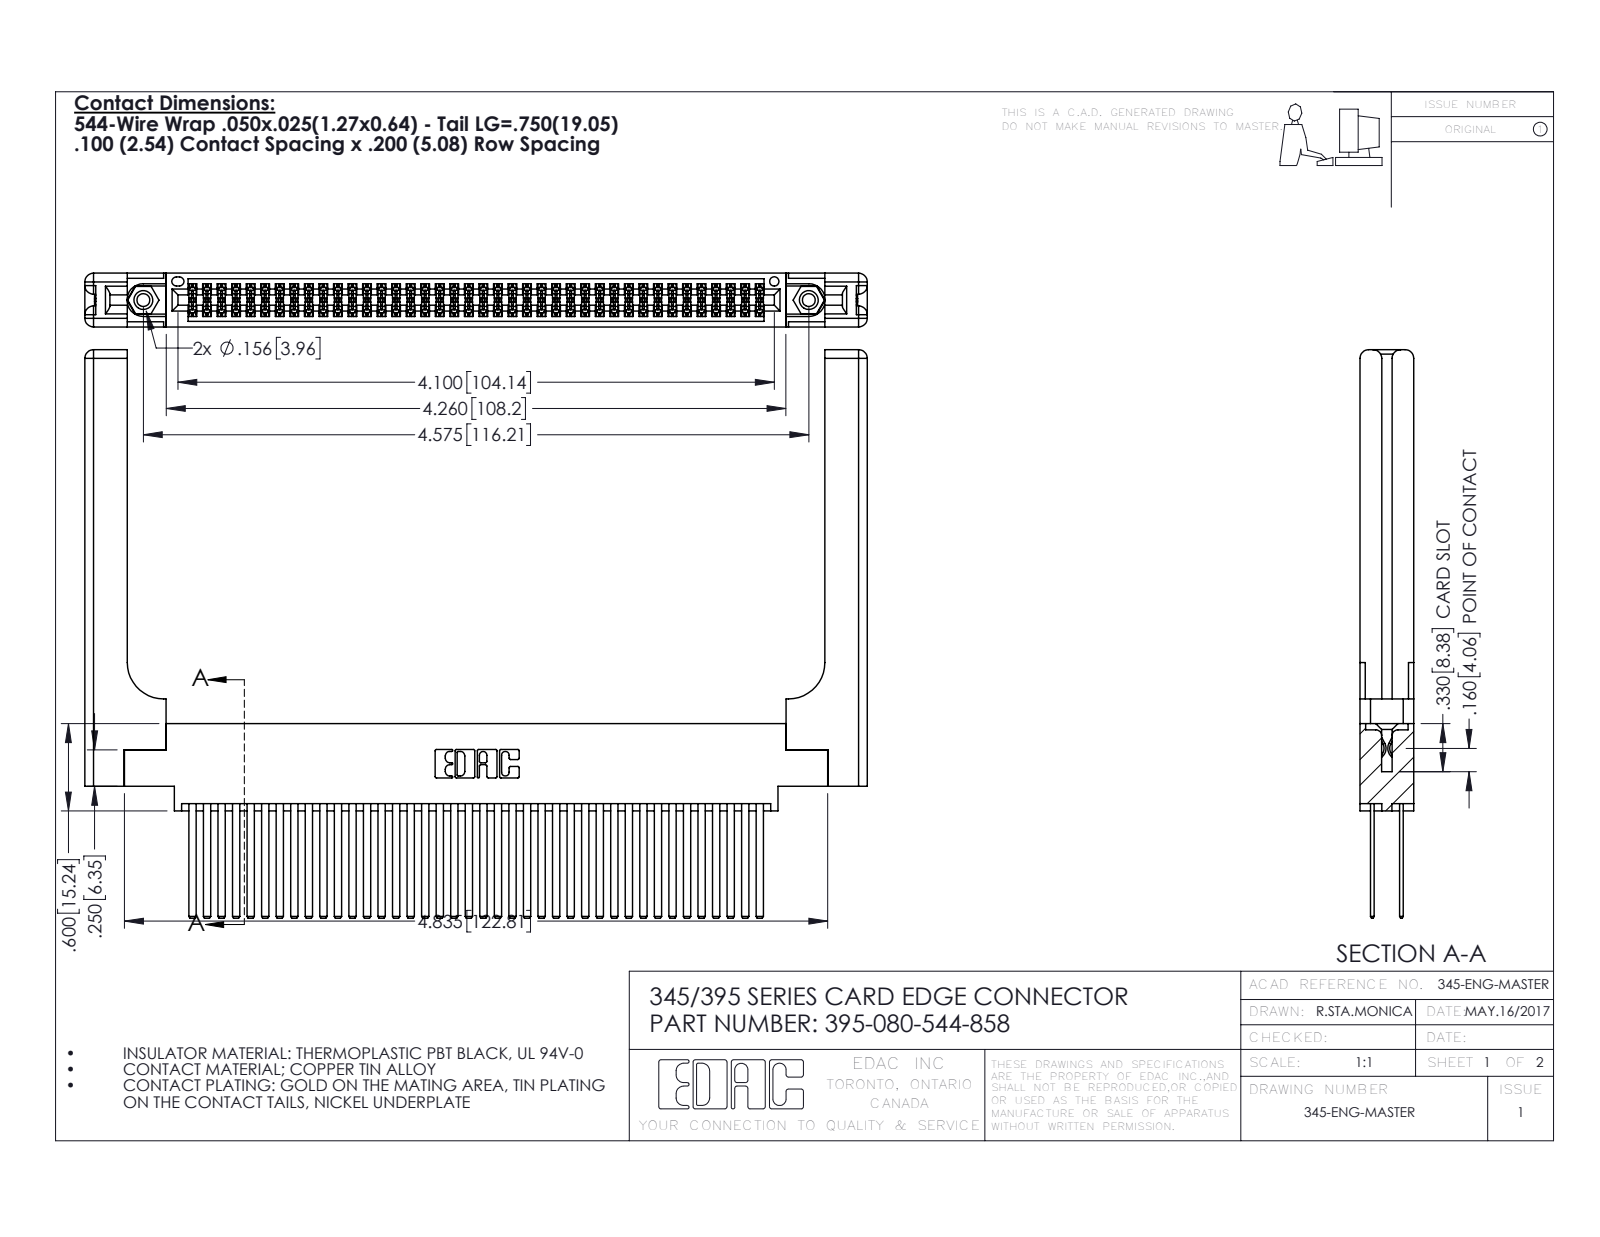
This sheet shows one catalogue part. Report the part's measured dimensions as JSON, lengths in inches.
{"part_name": "345-220-058_345-220-058; 345-292-001_345-293-144; 345-250-001_345-250-001-102; 395-080-544-858 (+1 more)", "step_written_by": "SolidWorks 2016 (CONFIG_CONTROL_DESIGN)", "units": "inches", "bodies": {"solids": 85, "faces": 3906, "planar": 2552, "cylindrical": 1294, "other": 60}, "overall_size": [5.379, 3.907, 0.37], "volume_in3": 1.387, "surface_area_in2": 45.77, "round_holes": [[0.089, 2], [0.125, 2], [0.156, 2], [0.064, 1]], "round_bosses_or_shafts": [[0.155, 2]], "partial_cylinders_radius": [[0.006, 120], [0.01, 22], [0.06, 16], [0.007, 6], [0.031, 6], [0.026, 3], [0.014, 2], [0.019, 2]], "face_to_face_distances": [0.072, 0.298, 0.098, 0.272, 0.025, 0.2, 0.37, 0.225, 0.175, 0.148], "hole_center_spacings": [0.27, 4.339, 4.575]}
